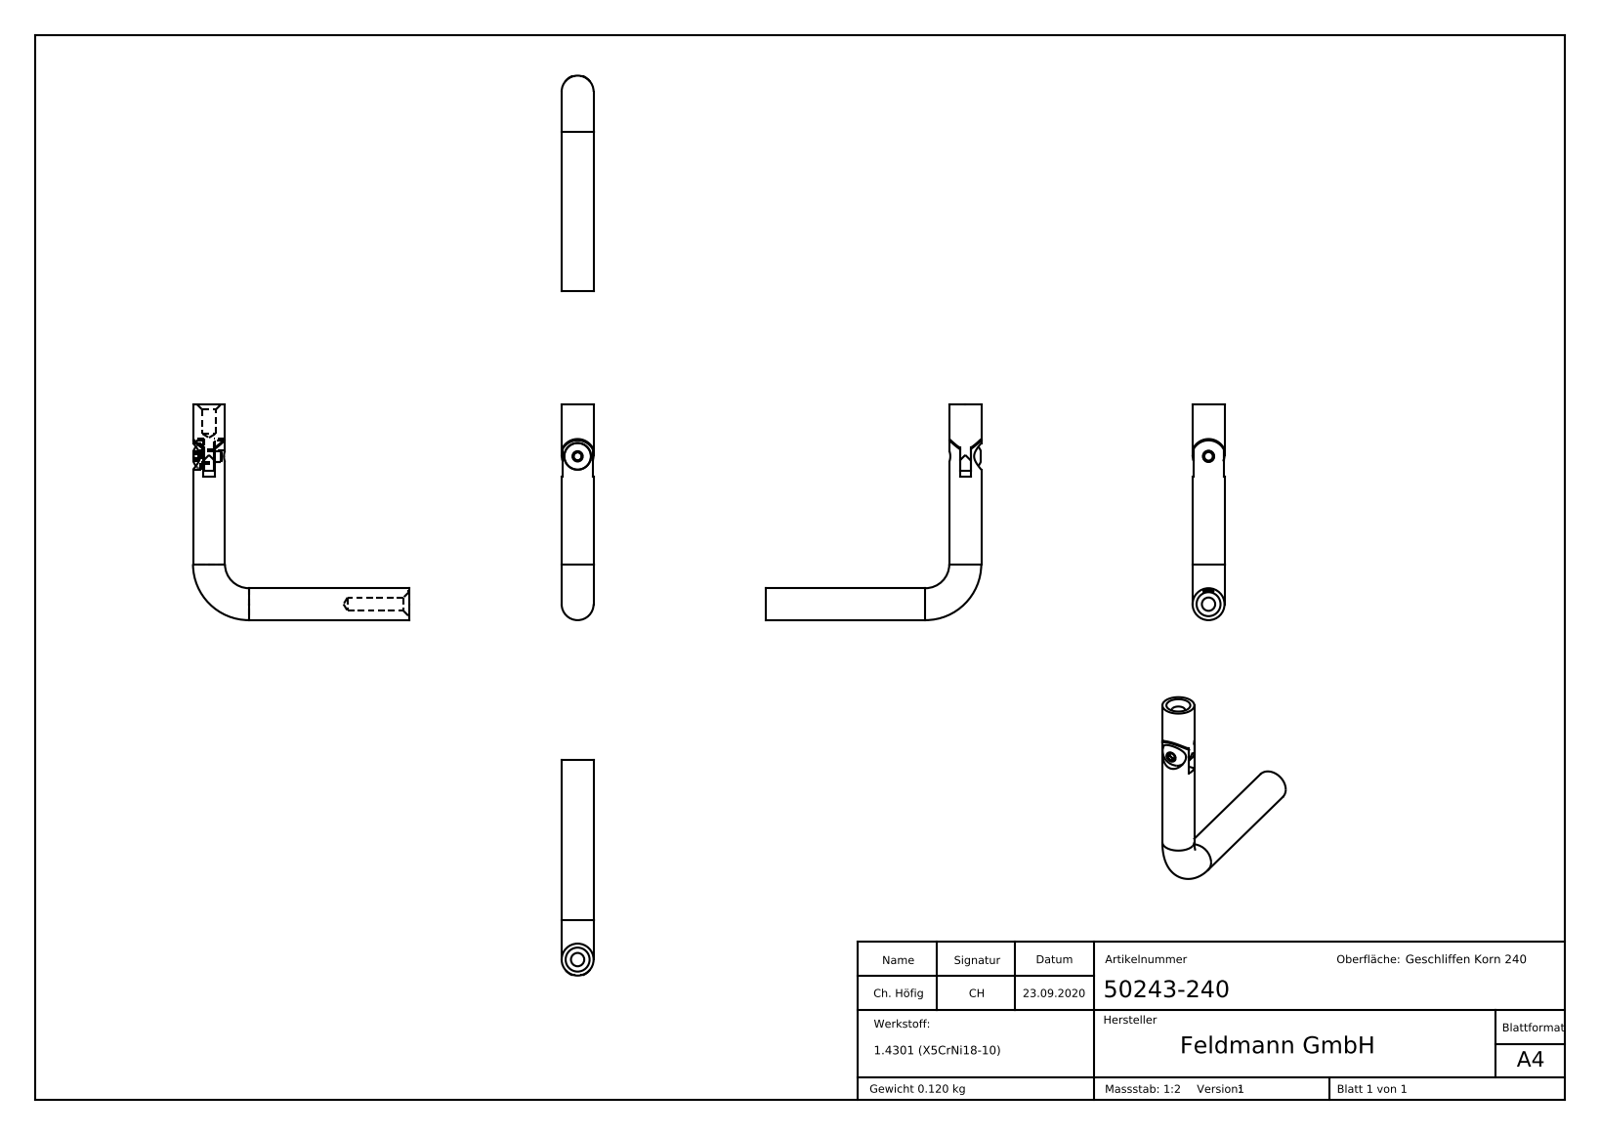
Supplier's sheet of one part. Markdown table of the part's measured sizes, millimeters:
| quantity | value |
| --- | --- |
| part name | 50243-240 Teil2; 50243-240 Teil3_M5x8; 50243-240 Teil3; 50243-240 (+3 more) |
| STEP written by | SolidWorks 2018 (CONFIG_CONTROL_DESIGN) |
| units | millimeters |
| bodies | 3 solids, 297 faces (147 planar, 27 cylindrical, 123 other) |
| overall size | 81 × 81 × 12 |
| volume | 15 140 mm³ |
| surface area | 7 215 mm² |
| round holes (diameter × count) | 5 × 2, 4.2 × 1, 5.5 × 1, 10 × 1 |
| round bosses / shafts (diameter × count) | 12 × 2, 4.02 × 1 |
| partial cylindrical surfaces (radius × count) | 6.5 × 2, 6 × 1 |
| main face-to-face distances | 4.05, 5.1, 4.1, 1, 1.05, 4, 5.05, 72.95, 73, 77 |
| hole center spacings | 55.5 |
